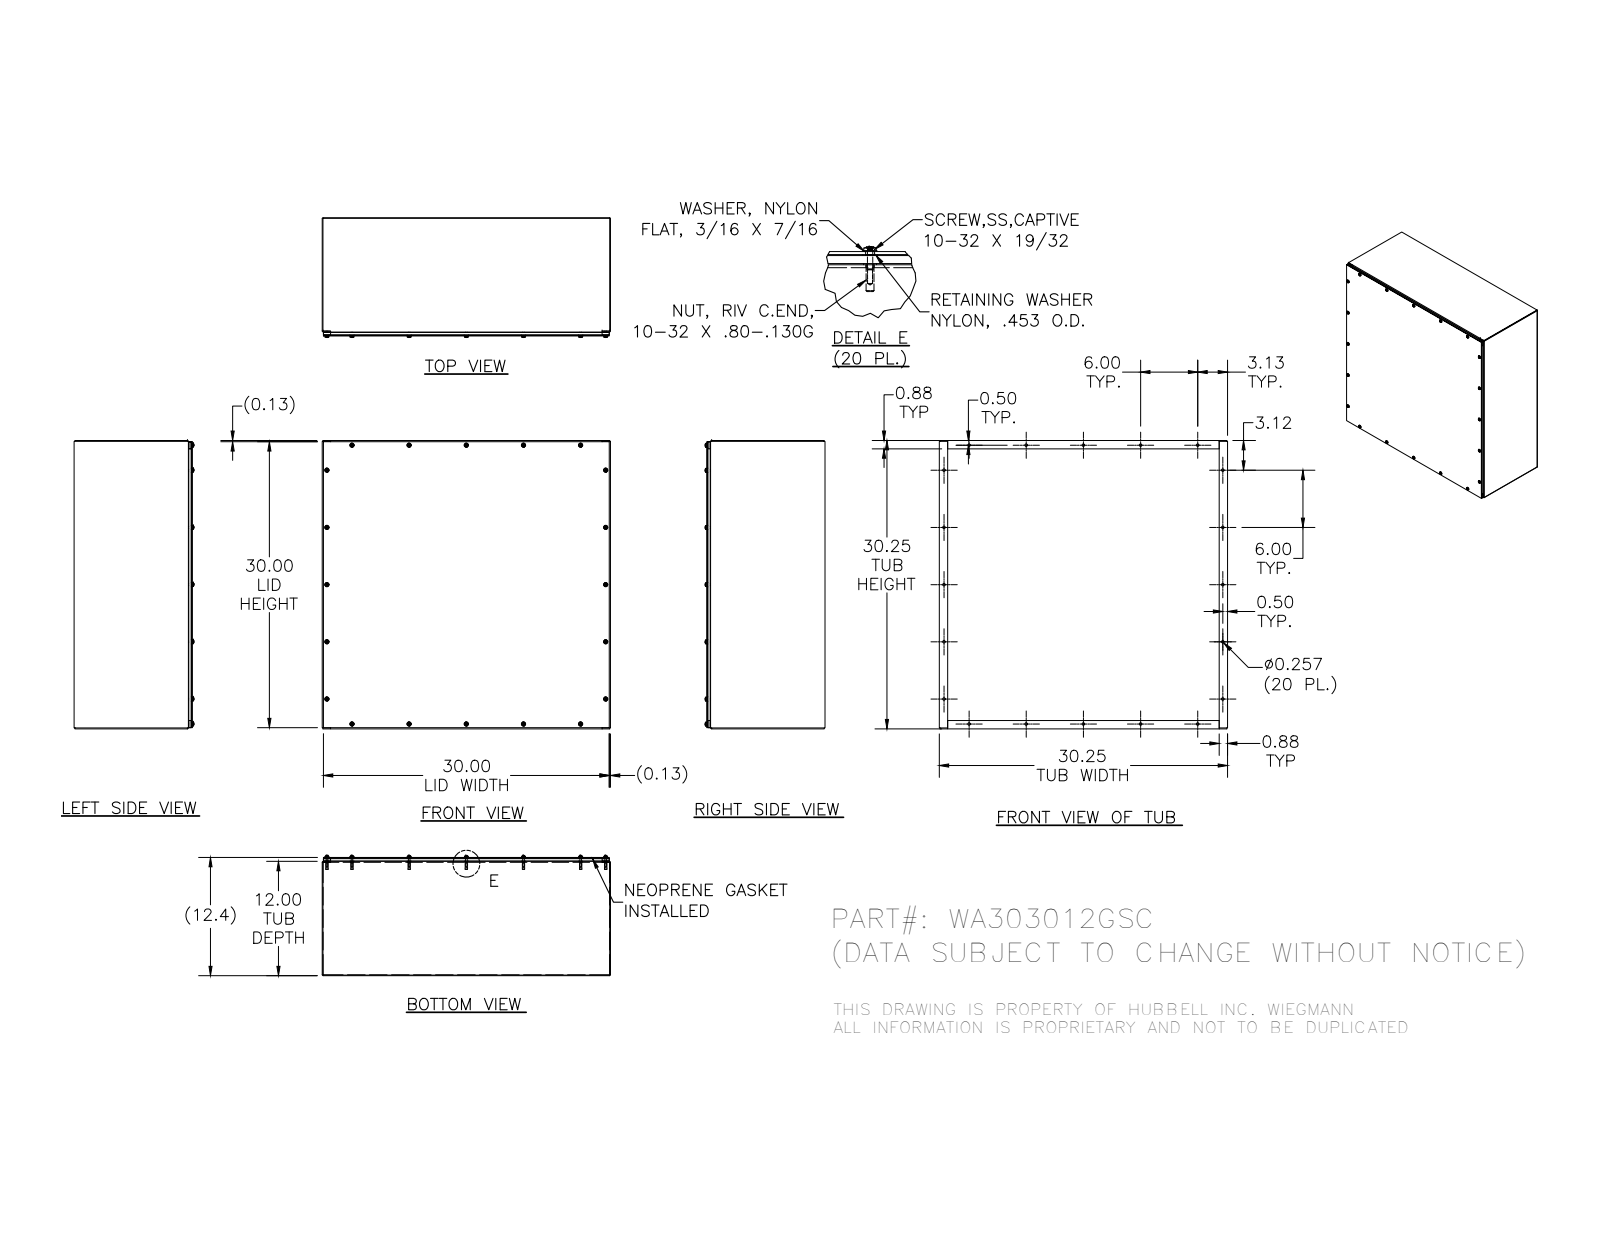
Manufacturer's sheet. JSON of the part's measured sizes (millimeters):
{"part_name": "WA303012GSCTEW; 37210; 34984; WA303012GSCBKP (+5 more)", "step_written_by": "SolidWorks 2014 (AUTOMOTIVE_DESIGN)", "units": "millimeters", "bodies": {"solids": 88, "faces": 2020, "planar": 948, "cylindrical": 532, "other": 540}, "overall_size": [768.4, 768.3, 319.2], "volume_mm3": 5501000, "surface_area_mm2": 4514000, "round_holes": [[4, 20], [4.8, 20], [5, 20], [6.5, 20], [7.1, 20], [7.1, 20]], "round_bosses_or_shafts": [[11.5, 20], [11.1, 20], [10.3, 20], [6.3, 20], [4.2, 20]], "partial_cylinders_radius": [[2.3, 20], [0.4, 6], [2.8, 6]], "face_to_face_distances": [2.4, 312.9, 310.5, 315.3, 2.4, 766, 763.6, 768.4, 766, 766], "hole_center_spacings": [758.4, 743, 152.4, 803, 304.8, 872.4, 457.2, 152.4]}
